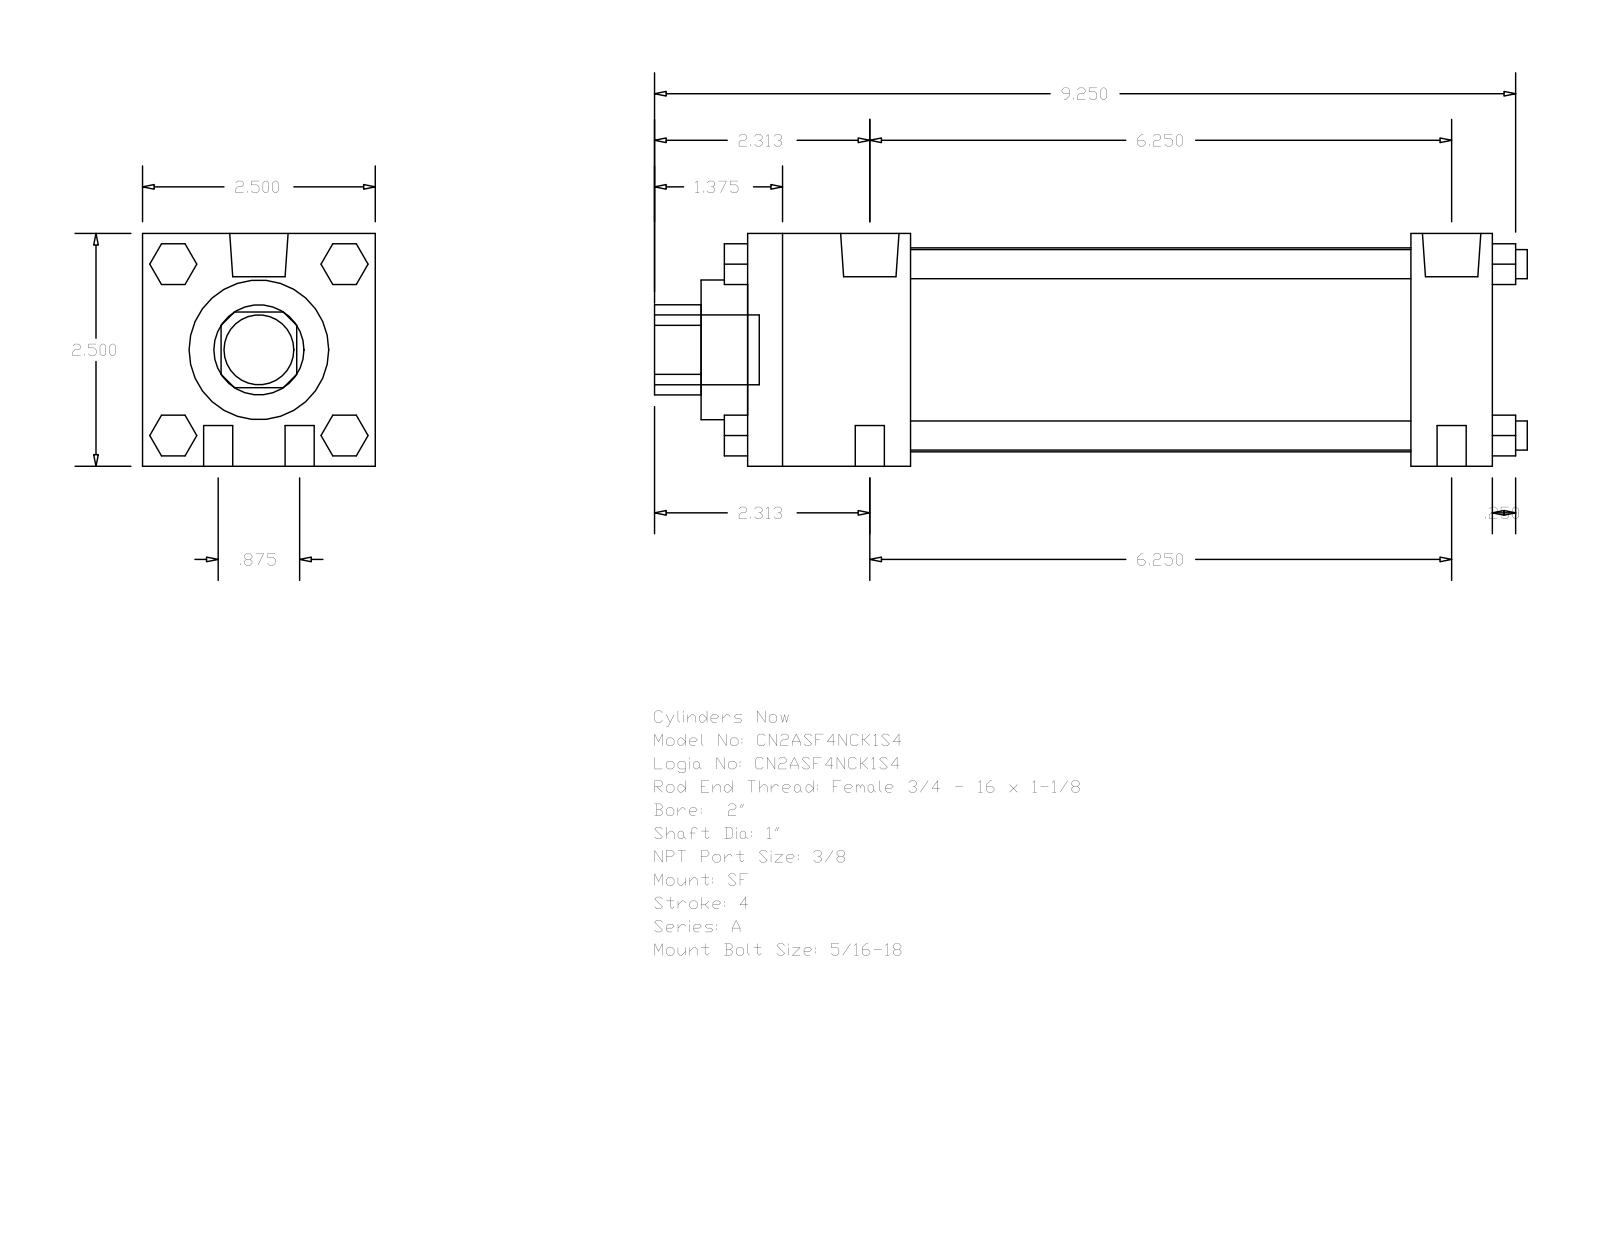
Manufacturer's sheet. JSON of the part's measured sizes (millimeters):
{"part_name": "A_SF__0200_1", "step_written_by": "GSSL Pune (CONFIG_CONTROL_DESIGN)", "units": "millimeters", "bodies": {"solids": 0, "faces": 124, "planar": 94, "cylindrical": 30, "other": 0}, "overall_size": [238.12, 63.5, 63.5], "round_holes": [[25.4, 1], [38.1, 1], [55.63, 1]], "round_bosses_or_shafts": [[7.94, 8], [15.93, 2], [5.56, 2], [19.05, 1]], "partial_cylinders_radius": [[12.29, 1]], "face_to_face_distances": [63.5, 203.2, 180.98, 22.22, 44.45, 136.53, 158.75, 12.7, 215.9, 6.35]}
